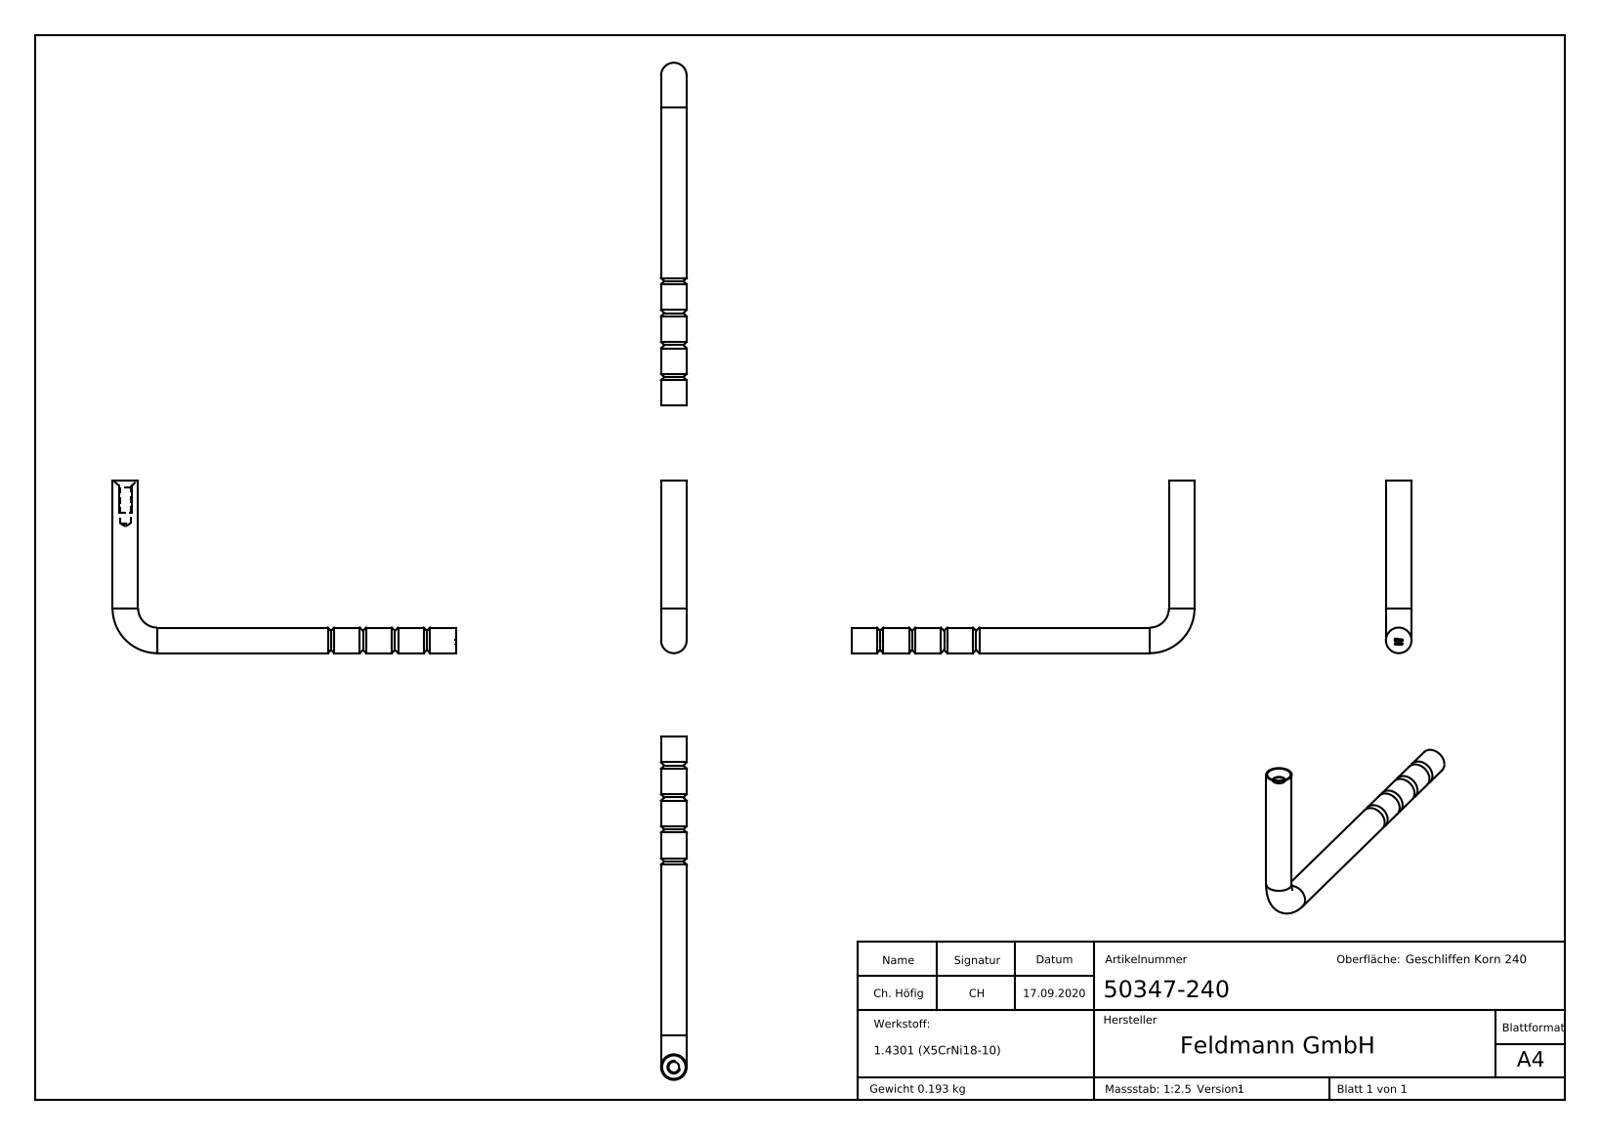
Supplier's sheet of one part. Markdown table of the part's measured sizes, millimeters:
| quantity | value |
| --- | --- |
| part name | 50347-240 |
| STEP written by | SolidWorks 2018 (CONFIG_CONTROL_DESIGN) |
| units | millimeters |
| bodies | 1 solid, 261 faces (131 planar, 14 cylindrical, 116 other) |
| overall size | 161 × 81 × 12 |
| volume | 24 472 mm³ |
| surface area | 9 067 mm² |
| round holes (diameter × count) | 5 × 1 |
| round bosses / shafts (diameter × count) | 12 × 2 |
| main face-to-face distances | 1.19, 1.46, 1.35, 0.53, 1.88, 1.47, 1.64, 1.2, 2.12, 0.66 |
